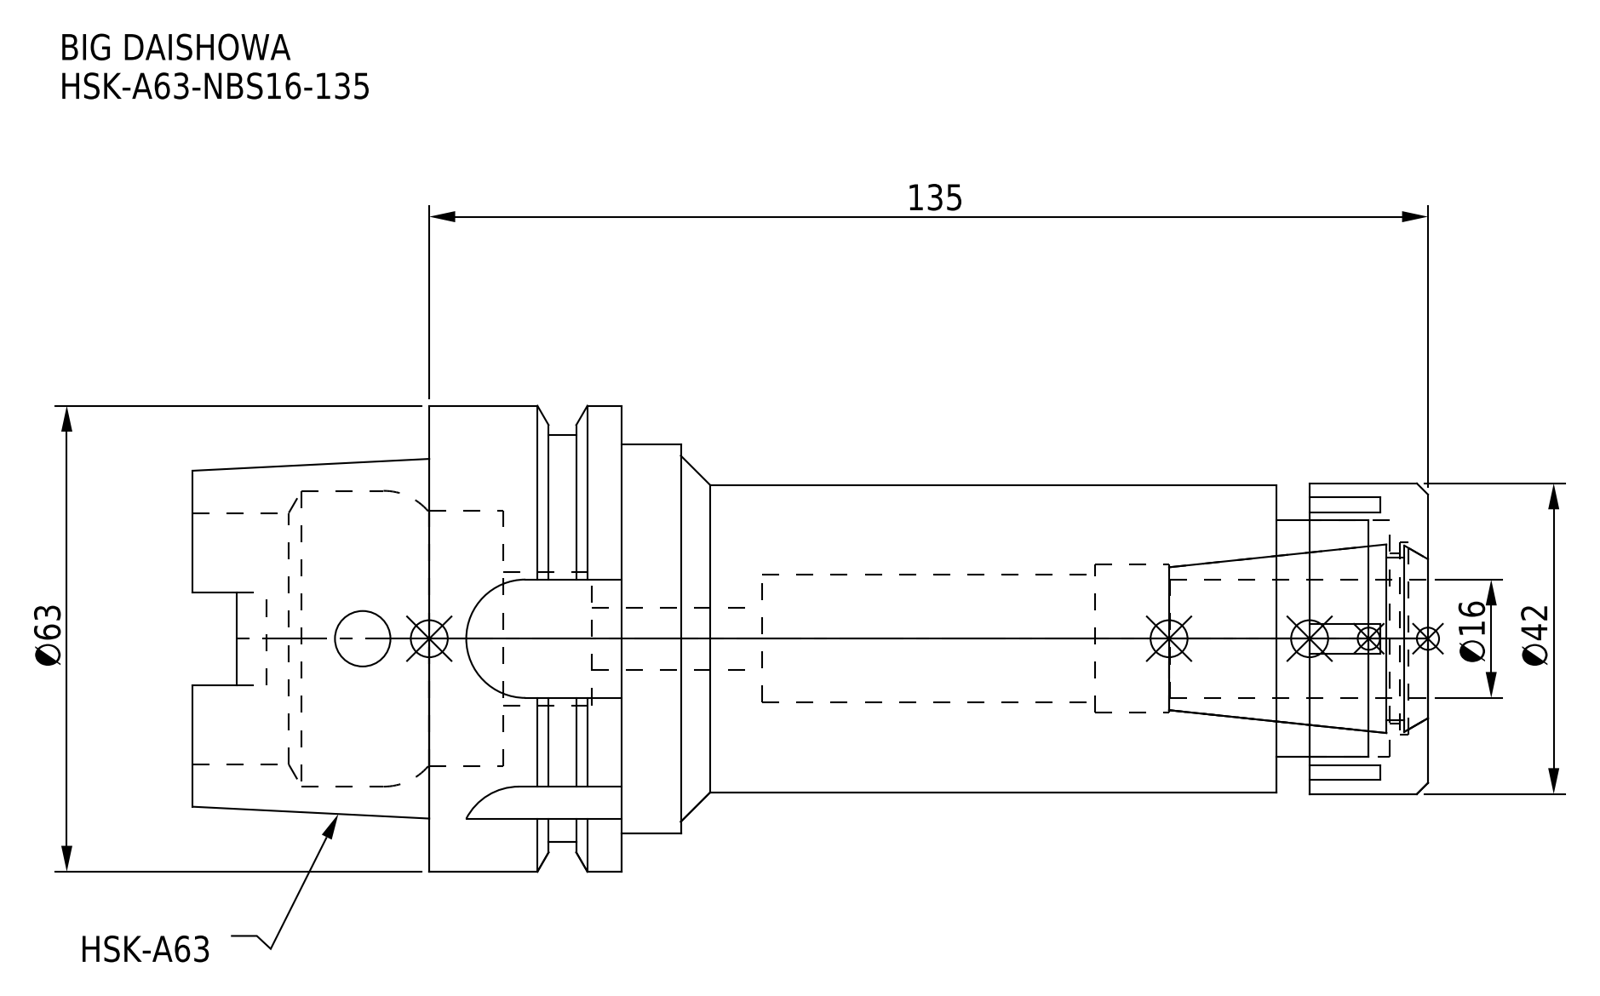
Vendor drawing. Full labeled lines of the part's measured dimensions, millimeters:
Part name (STEP PRODUCT): HSK-A63-NBS16-135; DXF_TEMP_ASSY_ASM_4_ASM.stp; NBN16_1.stp; HSK-A63-NBS16-135.stp (+3 more)
STEP written by: SolidWorks 2019 (CONFIG_CONTROL_DESIGN)
Units: millimetres
Bodies: 2 solids, 141 faces (70 planar, 49 cylindrical, 22 other)
Overall size (bounding box): 167 × 63 × 63
Volume: 204 289 mm³ · Surface area: 46 352 mm²
Round holes (diameter × count): ⌀7.5 ×1, ⌀8.4 ×1, ⌀17.3 ×1, ⌀18 ×1, ⌀20 ×1, ⌀23 ×1, ⌀26 ×1, ⌀32 ×1, ⌀34 ×1, ⌀34.5 ×1, ⌀40 ×1
Round bosses / shafts (diameter × count): ⌀63 ×1, ⌀55 ×1, ⌀52.6 ×1, ⌀42 ×1, ⌀41.5 ×1
Partial cylindrical surfaces — rounded edges, fillets, slot ends (radius × count): R2.88 ×4, R8 ×4
Main face-to-face distances: 8, 26, 135, 109, 93, 125.05, 16.05, 9.95, 101, 16
